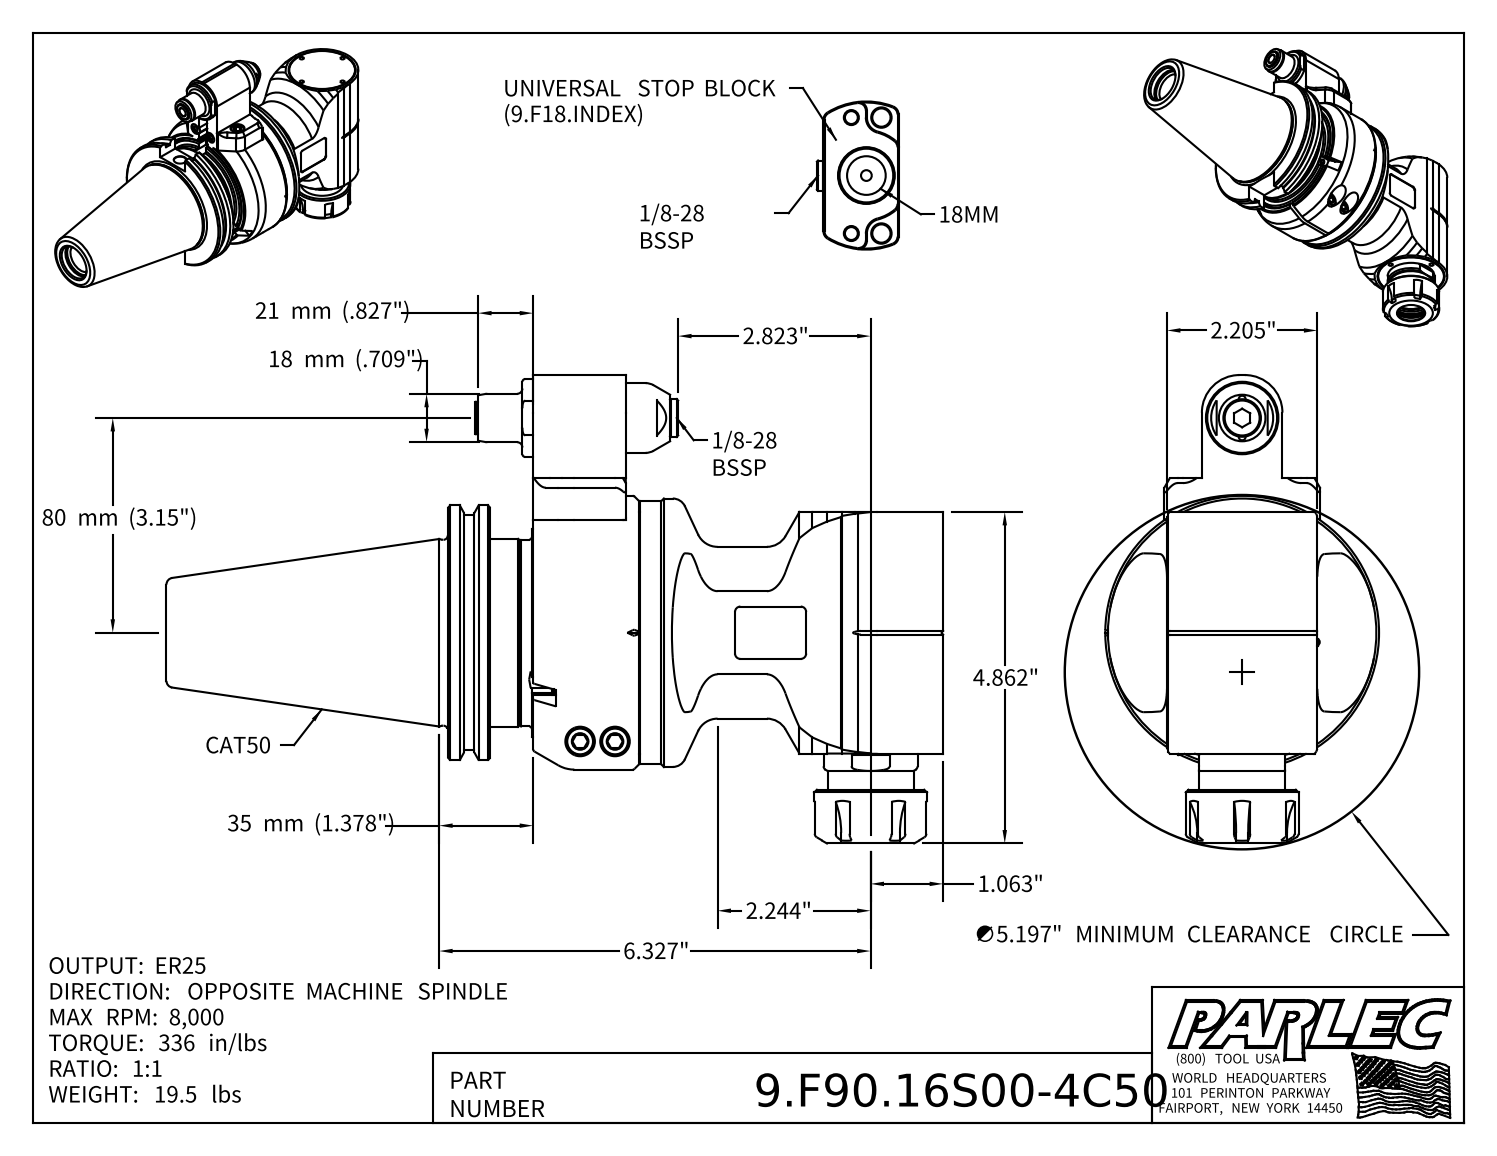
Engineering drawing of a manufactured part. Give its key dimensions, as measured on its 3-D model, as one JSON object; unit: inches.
{"part_name": "9.F90.16S00-4C50; 9_F90_16S00; 9GA11C_458 (EVO, Type 1, Cat50, 80mm)", "step_written_by": "Autodesk Inventor 2022 (AUTOMOTIVE_DESIGN)", "units": "inches", "bodies": {"solids": 4, "faces": 613, "planar": 278, "cylindrical": 160, "other": 175}, "overall_size": [11.39, 6.87, 4.016], "volume_in3": 77.75, "surface_area_in2": 257.3, "round_holes": [[0.126, 4], [0.256, 3], [0.102, 2], [0.13, 2], [0.165, 2], [0.197, 2], [0.315, 2], [0.409, 2], [0.433, 2], [0.492, 2], [1.063, 2], [0.098, 1]], "round_bosses_or_shafts": [[0.394, 4], [0.709, 2], [0.472, 2], [0.315, 2], [0.236, 2], [0.098, 2], [4.016, 1], [3.937, 1]], "partial_cylinders_radius": [[0.039, 14], [0.079, 12], [0.118, 6], [0.984, 6], [0.157, 4], [0.016, 2], [0.02, 2], [0.315, 2]], "face_to_face_distances": [1.28, 1.252, 0.028, 2.183, 0.931, 0.904, 2.808, 1.556, 1.528, 0.625], "hole_center_spacings": [0.846, 1.197, 0.276, 0.959, 1.222, 1.49, 1.693, 1.994]}
